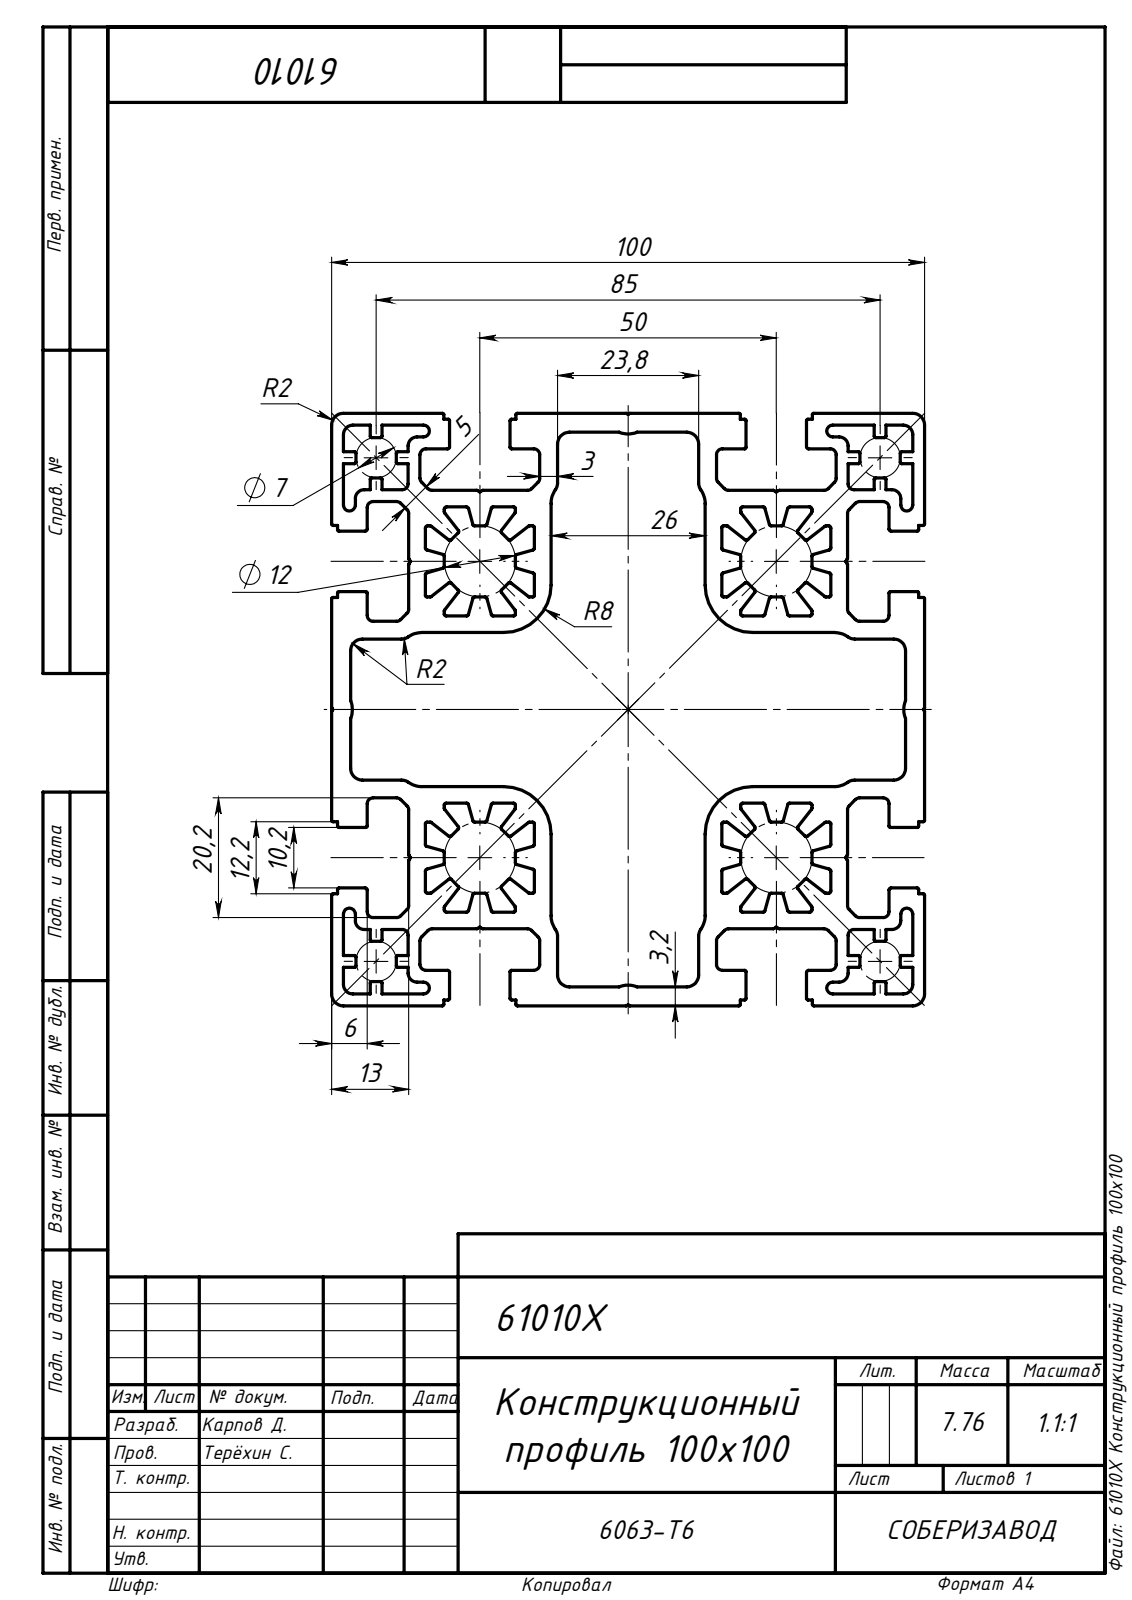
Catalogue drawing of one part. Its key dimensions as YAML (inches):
part_name: "61010X Конструкционный профиль 100х100"
step_written_by: "SolidWorks 2019 (AUTOMOTIVE_DESIGN)"
units: inches
bodies: {solids: 1, faces: 814, planar: 426, cylindrical: 388, other: 0}
overall_size: [39.37, 3.937, 3.937]
volume: 175.4
surface_area: 2824
partial_cylinders:
  - {radius: 0.012, count: 120}
  - {radius: 0.01, count: 112}
  - {radius: 0.039, count: 60}
  - {radius: 0.016, count: 24}
  - {radius: 0.079, count: 20}
  - {radius: 0.157, count: 12}
  - {radius: 0.014, count: 8}
  - {radius: 0.059, count: 8}
face_to_face_distances: [0.11, 1.969, 3.937, 2.354, 0.386, 0.512, 3.425, 1.22, 3.189, 1.457]
